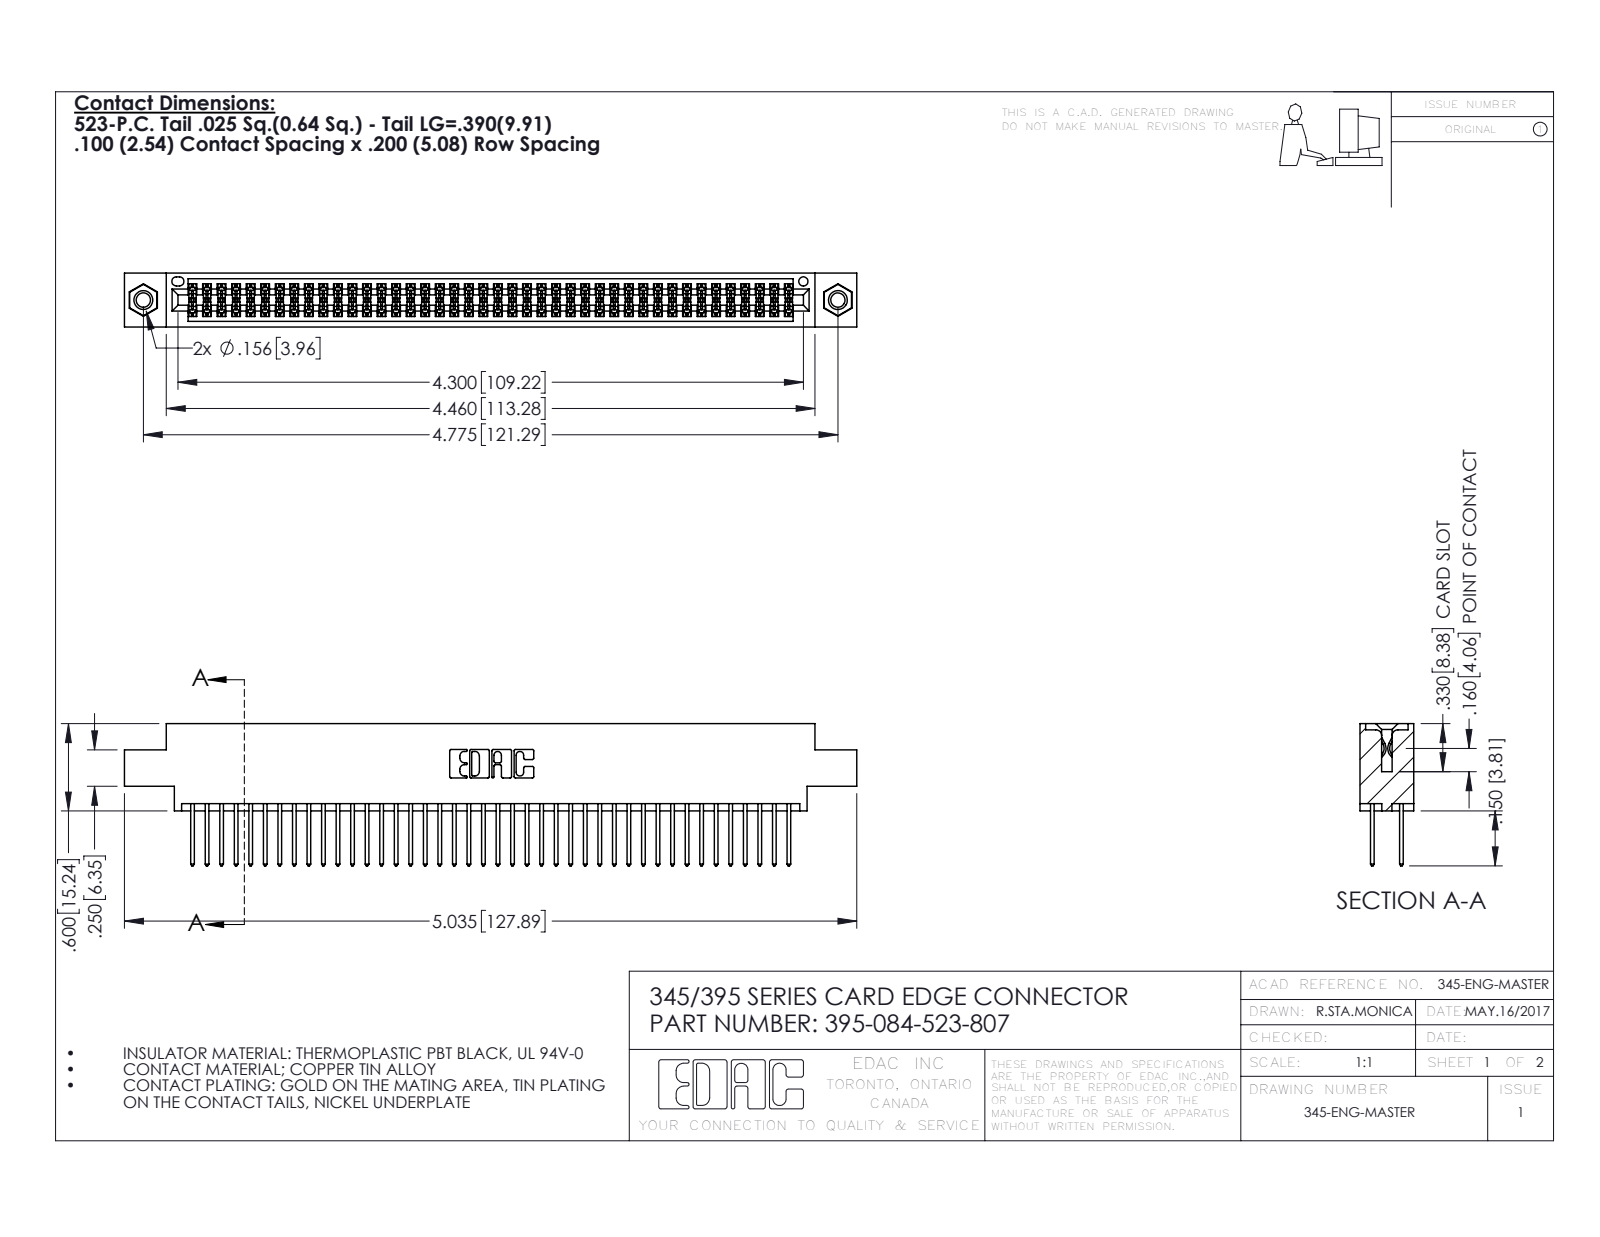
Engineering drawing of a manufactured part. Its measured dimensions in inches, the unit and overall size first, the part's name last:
Units: inches
Overall size (bounding box): 5.035 × 0.977 × 0.37
Round holes (diameter × count): ⌀0.098 ×2, ⌀0.125 ×2, ⌀0.156 ×2, ⌀0.064 ×1
Round bosses / shafts (diameter × count): ⌀0.155 ×2
Partial cylindrical surfaces — rounded edges, fillets, slot ends (radius × count): R0.006 ×126, R0.01 ×84, R0.01 ×22, R0.007 ×6, R0.031 ×6, R0.026 ×3, R0.014 ×2, R0.019 ×2
Main face-to-face distances: 0.072, 0.298, 0.2, 0.098, 0.272, 0.025, 0.37, 0.225, 0.175, 0.149
Hole centre spacings: 0.27, 4.539, 4.775
Volume: 0.761 in³ · Surface area: 30.03 in²
Bodies: 87 solids, 4390 faces (2888 planar, 1486 cylindrical, 16 other)
Part name (STEP PRODUCT): 345-250-001_345-250-005-103; 395-084-523-807; 345 Part_0.170 Offset - 0.156 Dia-TI; 345-292-001_345-293-123
STEP written by: SolidWorks 2016 (CONFIG_CONTROL_DESIGN)
